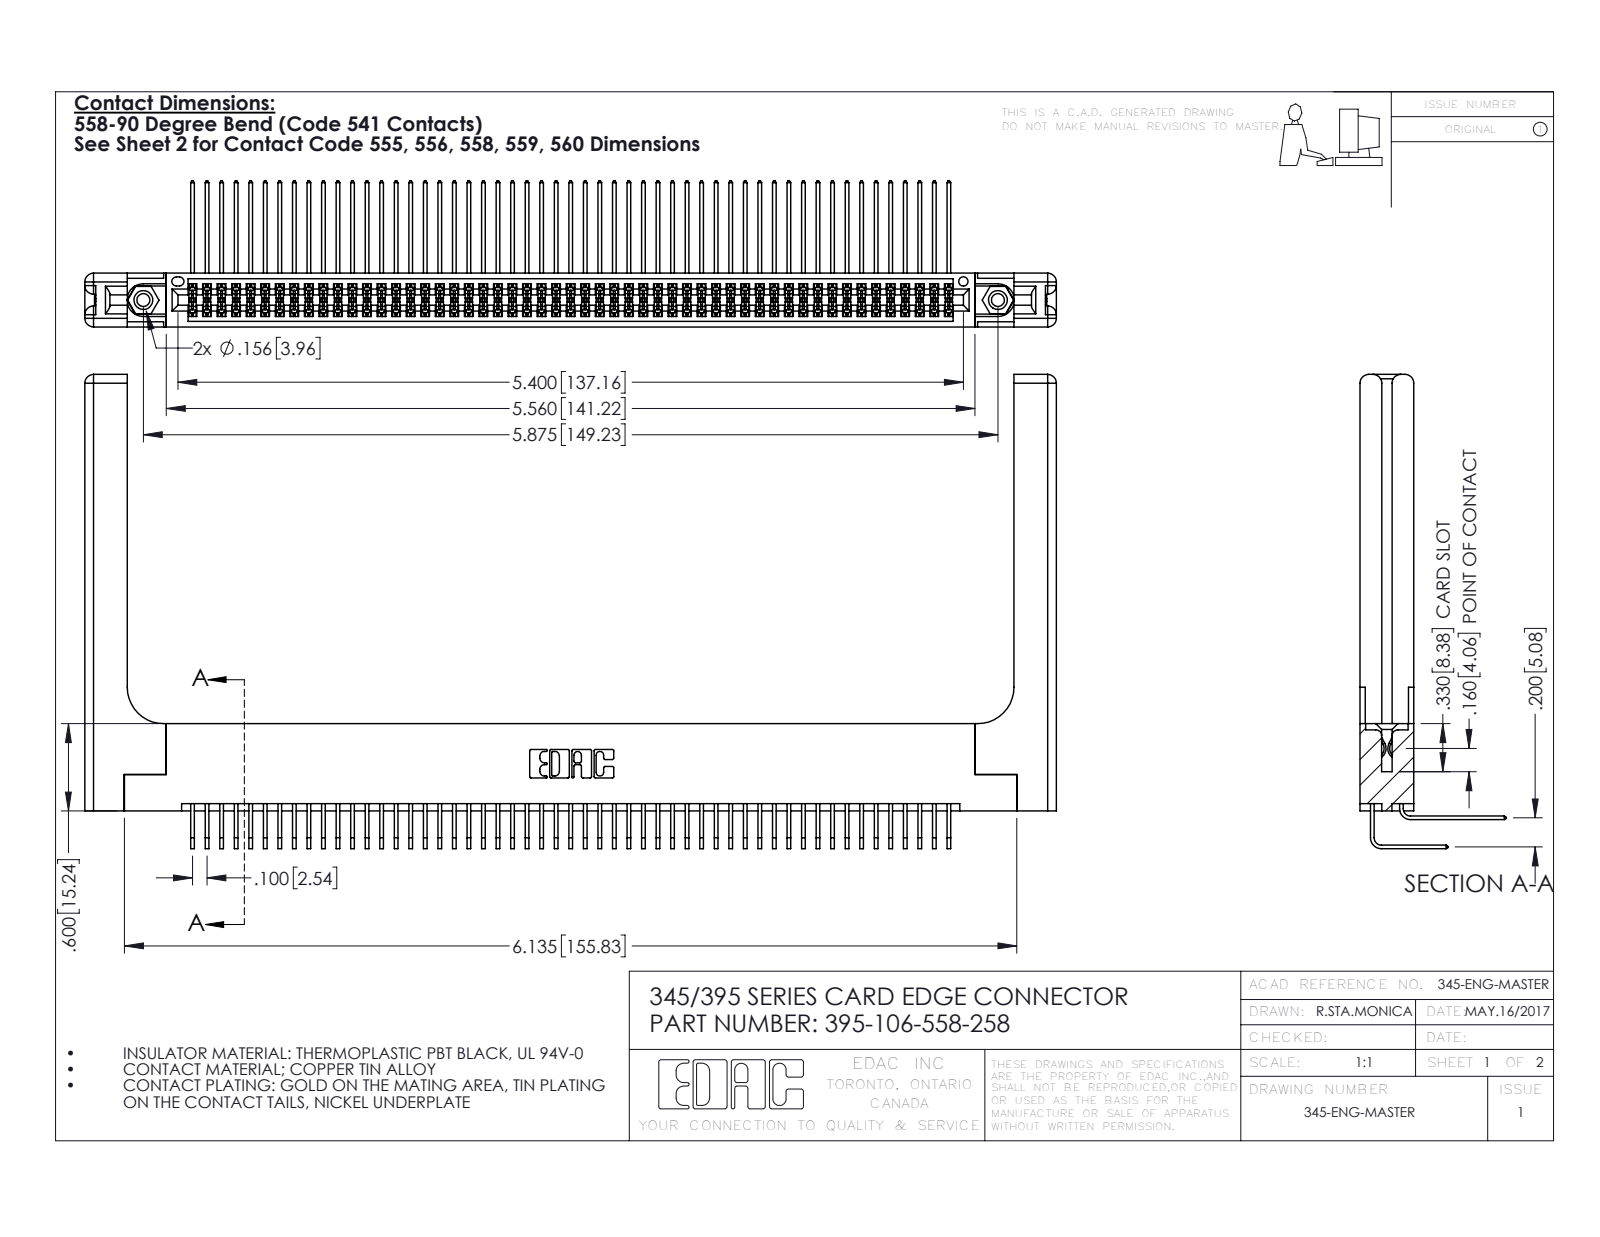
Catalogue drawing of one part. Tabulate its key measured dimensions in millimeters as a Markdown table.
| quantity | value |
| --- | --- |
| part name | 345-292-001_558 Tail - 2; 345-292-001_558 559 Tail - 1; 345-220-058_345-220-058; 345-250-001_345-250-001-102 (+2 more) |
| STEP written by | SolidWorks 2016 (CONFIG_CONTROL_DESIGN) |
| units | millimeters |
| bodies | 111 solids, 5894 faces (3938 planar, 1896 cylindrical, 60 other) |
| overall size | 169.6 × 82.8 × 25.5 |
| volume | 25 660 mm³ |
| surface area | 33 560 mm² |
| round holes (diameter × count) | 2.3 × 2, 3.2 × 2, 4 × 2, 1.6 × 1 |
| round bosses / shafts (diameter × count) | 3.9 × 2 |
| partial cylindrical surfaces (radius × count) | 0.2 × 160, 0.3 × 22, 1.5 × 16, 0.2 × 6, 0.8 × 6, 0.7 × 3, 0.4 × 2, 0.5 × 2 |
| main face-to-face distances | 1.8, 7.6, 9.4, 5.1, 2.5, 6.9, 0.6, 5.7, 3.8, 3.8 |
| hole center spacings | 6.9, 143.2, 149.2 |
